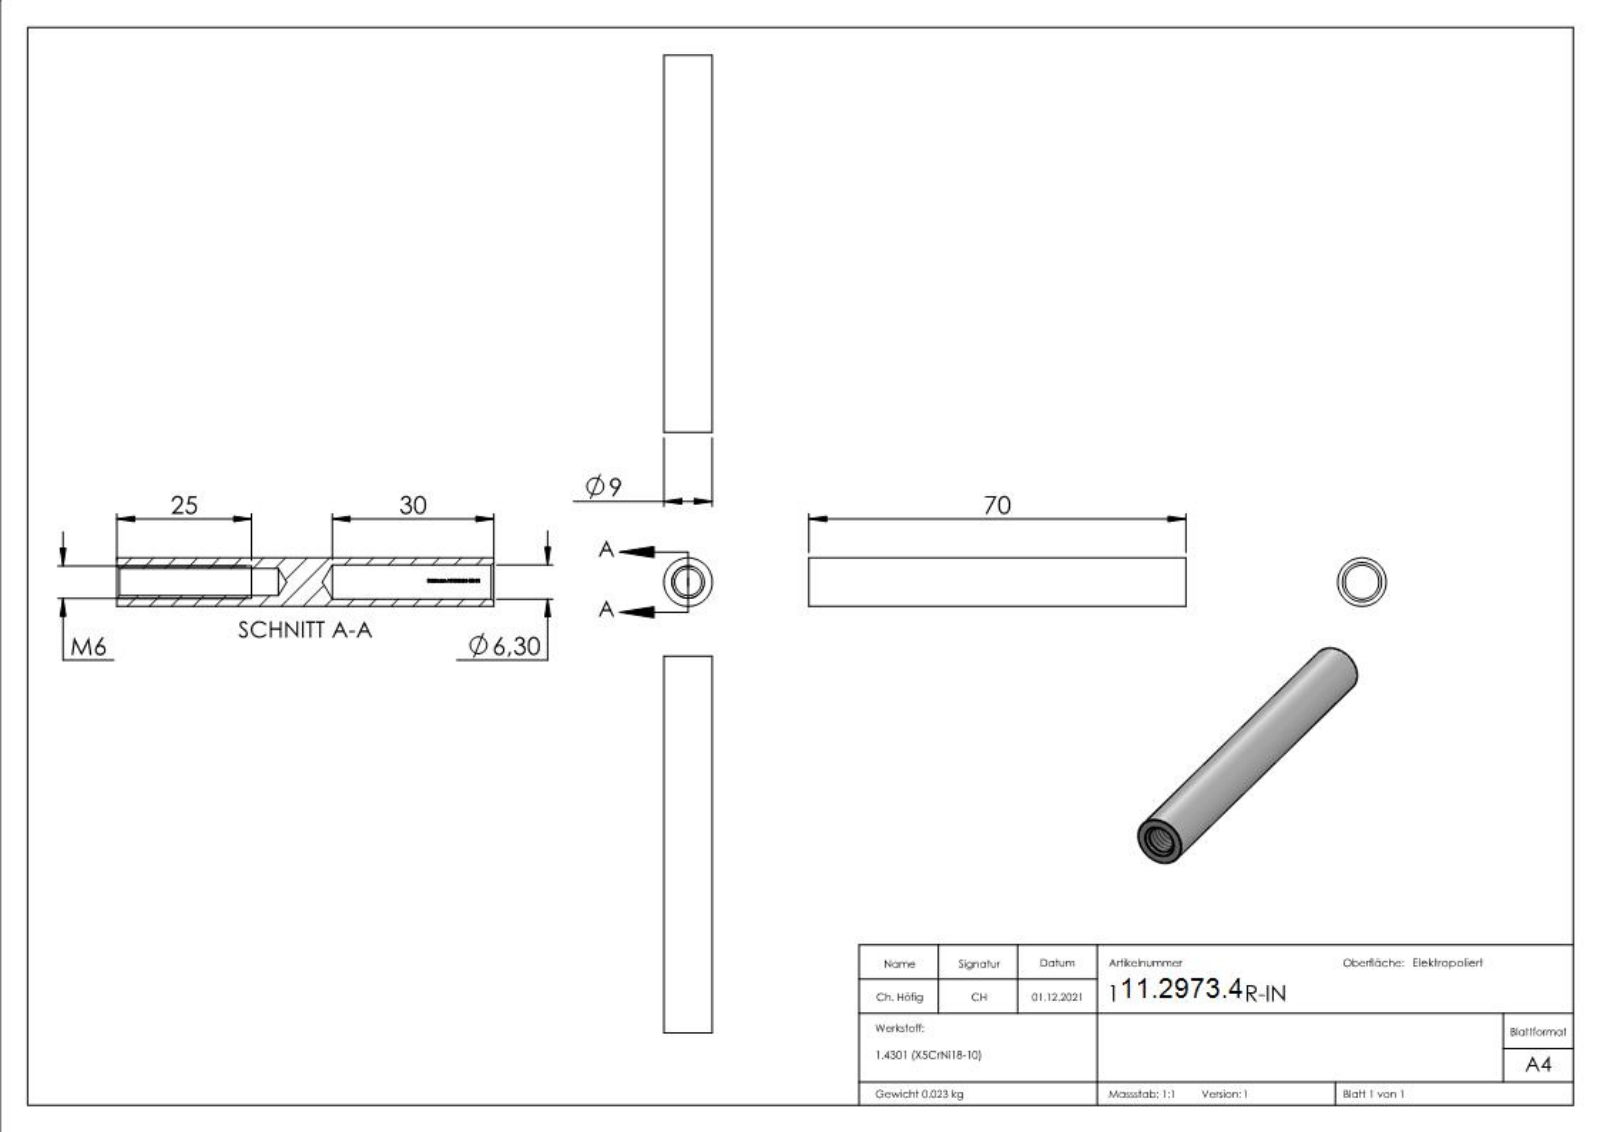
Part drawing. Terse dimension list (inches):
name: 101000606-GR-IN
written by: SolidWorks 2018 (CONFIG_CONTROL_DESIGN)
unit: in
bodies: 1 solid, 277 faces (111 planar, 37 cylindrical, 129 other)
size: 2.756 × 0.354 × 0.354
volume: 0.177 in³; area: 4.921 in²
holes: 1× ⌀0.197, 1× ⌀0.248
bosses: 1× ⌀0.354
rounds: 1× R0.128
face distances: 2.756, 0.022, 0.324, 0.02, 0.153, 0.032, 0.121, 0.155, 0.297, 0.295
